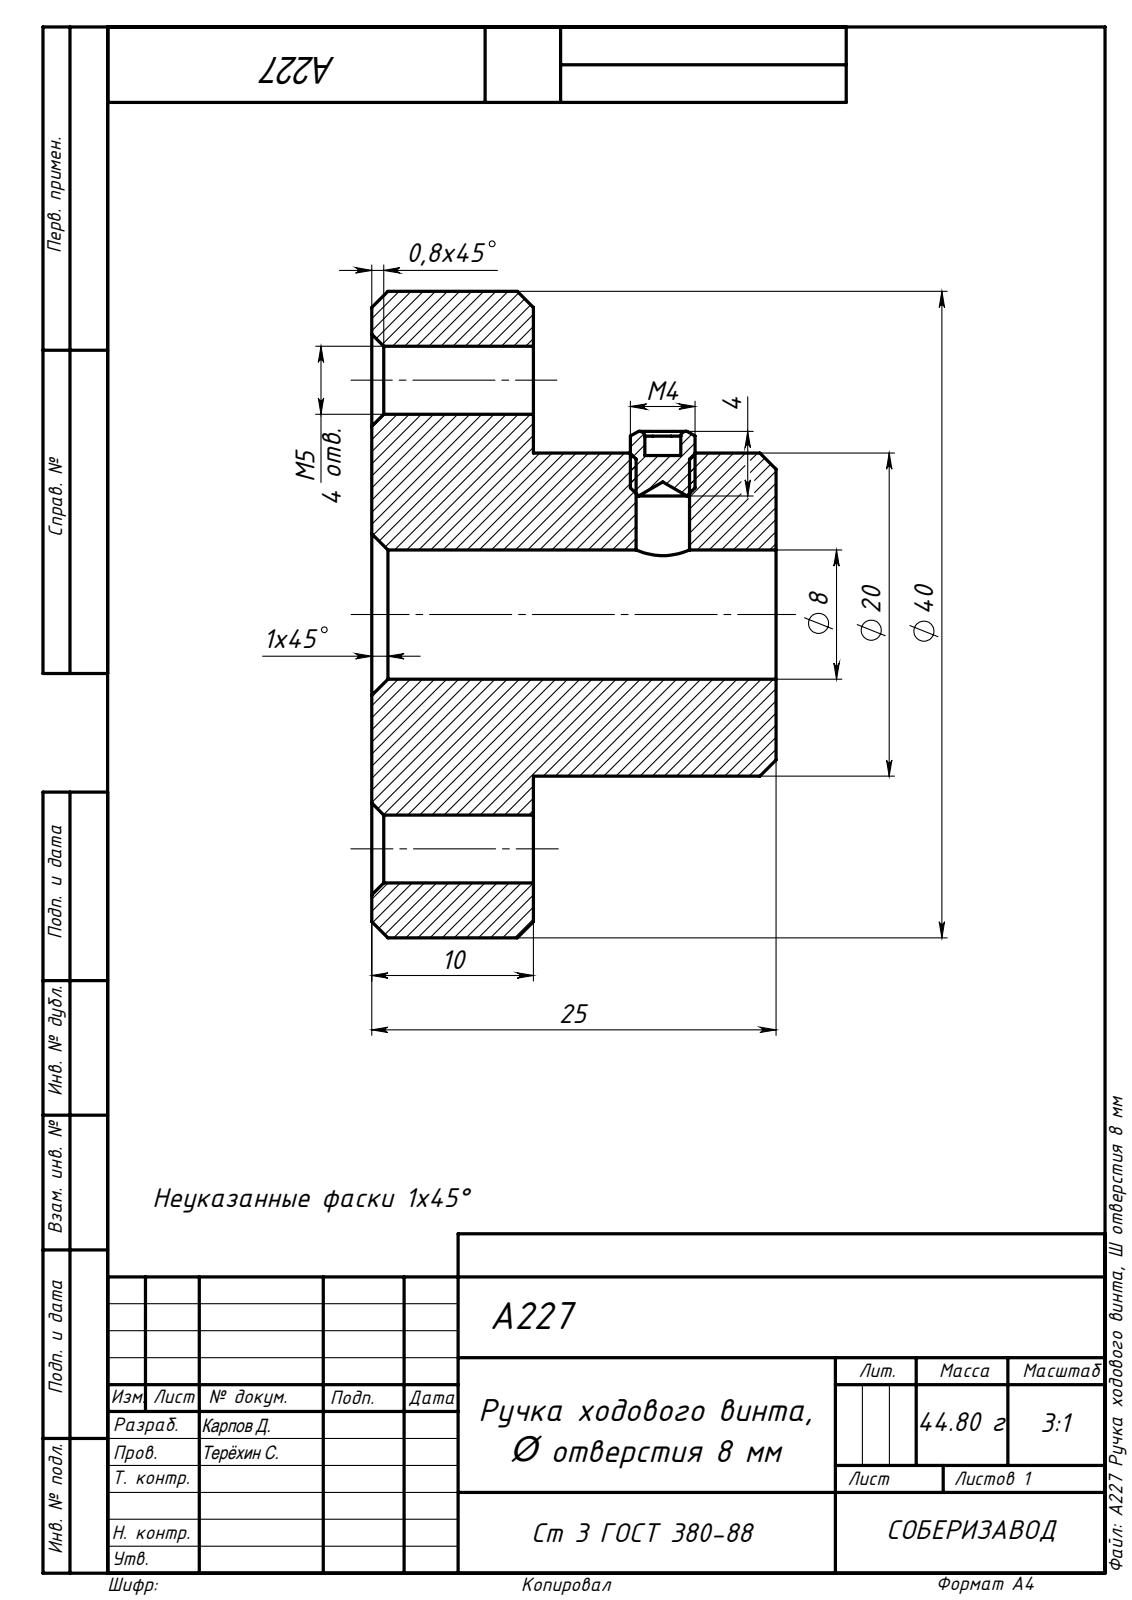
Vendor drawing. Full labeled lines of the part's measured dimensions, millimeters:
Part name (STEP PRODUCT): S54 Винт установочный DIN 916 М4 х 4_M4(4); A227 Ручка ходового винта, O отверстия 8 мм
STEP written by: SolidWorks 2020 (AUTOMOTIVE_DESIGN)
Units: millimetres
Bodies: 3 solids, 85 faces (19 planar, 34 cylindrical, 32 other)
Overall size (bounding box): 40 × 40 × 25
Volume: 15 261 mm³ · Surface area: 5 682 mm²
Round holes (diameter × count): ⌀4.2 ×4, ⌀3.3 ×2, ⌀8 ×1
Round bosses / shafts (diameter × count): ⌀4 ×2, ⌀40 ×1, ⌀20 ×1
Partial cylindrical surfaces — rounded edges, fillets, slot ends (radius × count): R0.3 ×12
Main face-to-face distances: 10, 15, 25, 1.99, 2, 1.5, 1.98
Hole centre spacings: 14.5, 20.51, 29
